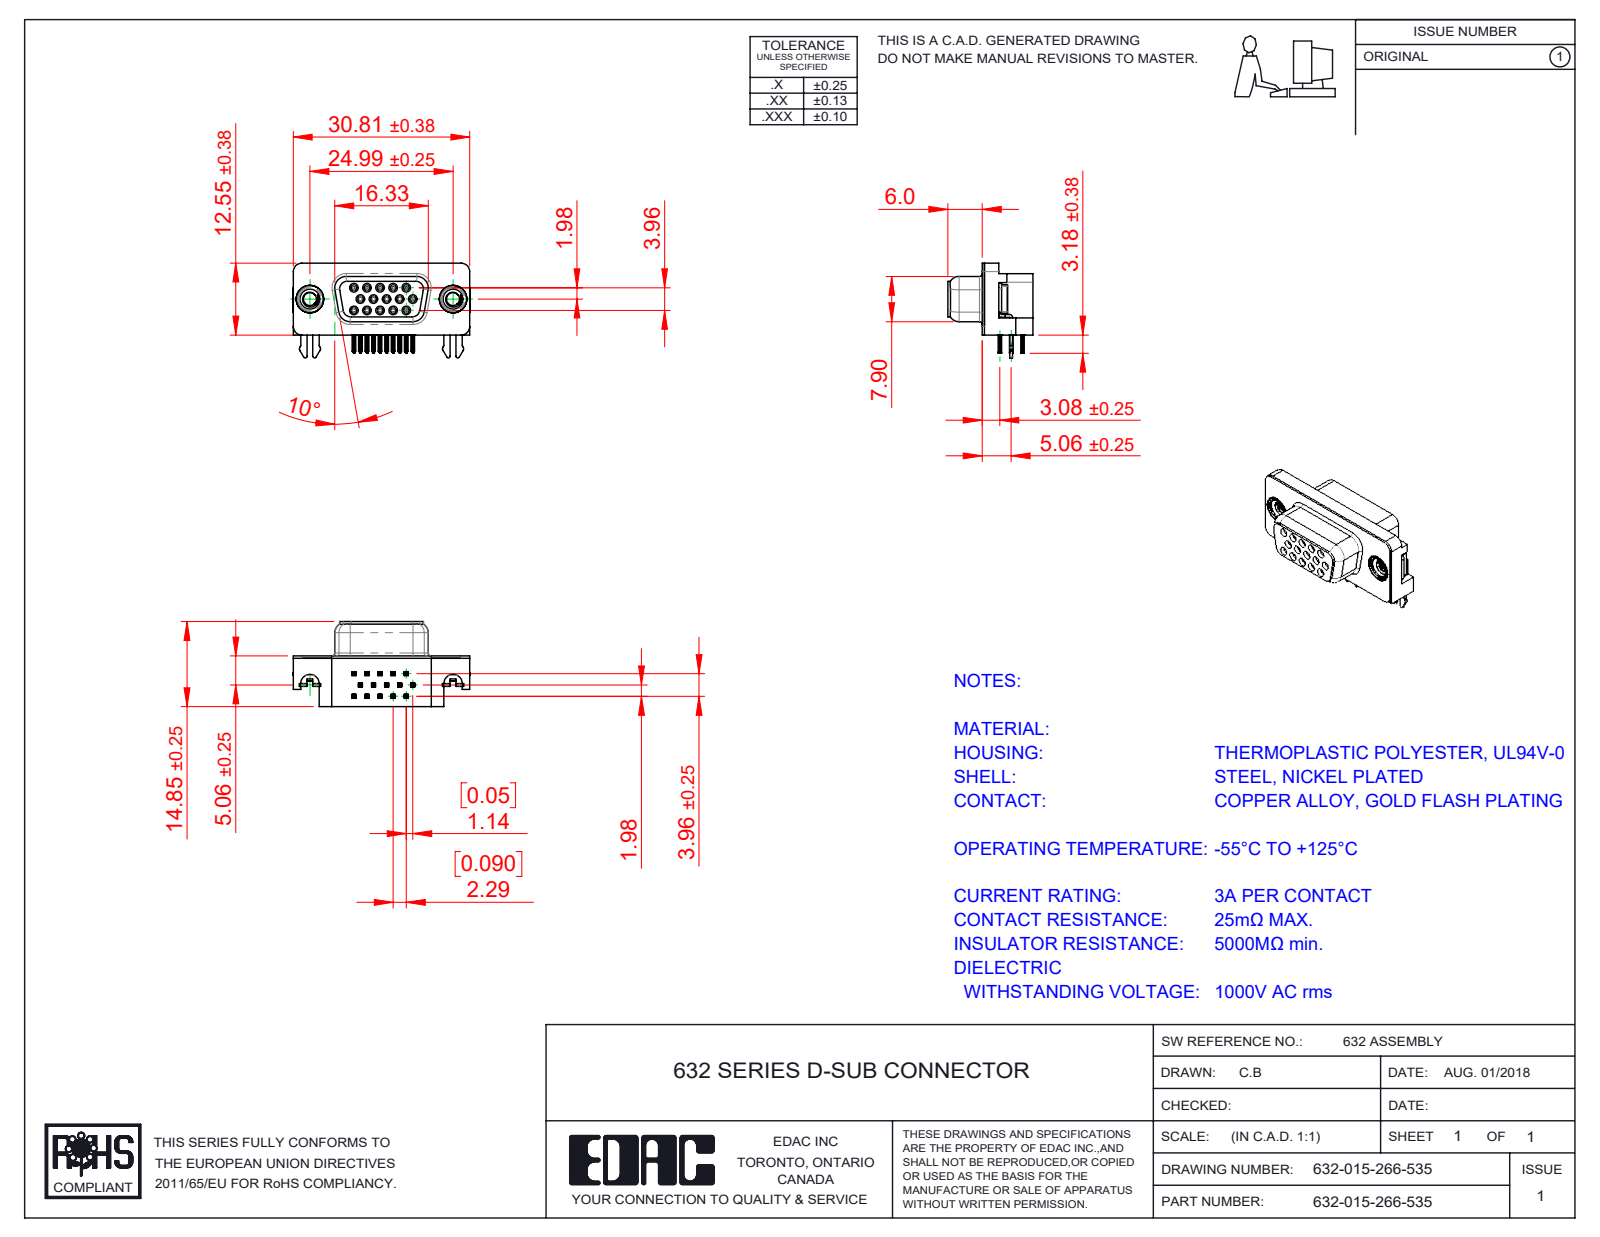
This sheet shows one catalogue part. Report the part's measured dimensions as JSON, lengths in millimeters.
{"part_name": "632 Contact Middle; 632 Shell_9 Socket; 632 4-40 Threaded Rivet; 632 2 Prong Board Lock (+5 more)", "step_written_by": "SolidWorks 2016 (CONFIG_CONTROL_DESIGN)", "units": "millimeters", "bodies": {"solids": 23, "faces": 2426, "planar": 1006, "cylindrical": 654, "other": 766}, "overall_size": [30.89, 16.55, 14.85], "volume_mm3": 2996, "surface_area_mm2": 5342, "round_holes": [[0.8, 15], [0.9, 15], [2.26, 2], [2.5, 2], [4, 2], [4.8, 2], [5, 2]], "round_bosses_or_shafts": [[1.2, 15], [4.9, 2], [4.75, 2], [3.9, 2]], "partial_cylinders_radius": [[0.1, 120], [0.15, 60], [0.35, 30], [0.34, 15], [1, 11], [0.28, 10], [0.5, 10], [0.25, 8]], "face_to_face_distances": [0.4, 8.45, 8.85, 1.98, 2.9, 5.95, 2.5, 6.4, 6.7, 7.05], "hole_center_spacings": [2.28, 2.29, 3.96, 4.57, 6.05, 3.97, 4.58, 6.86]}
